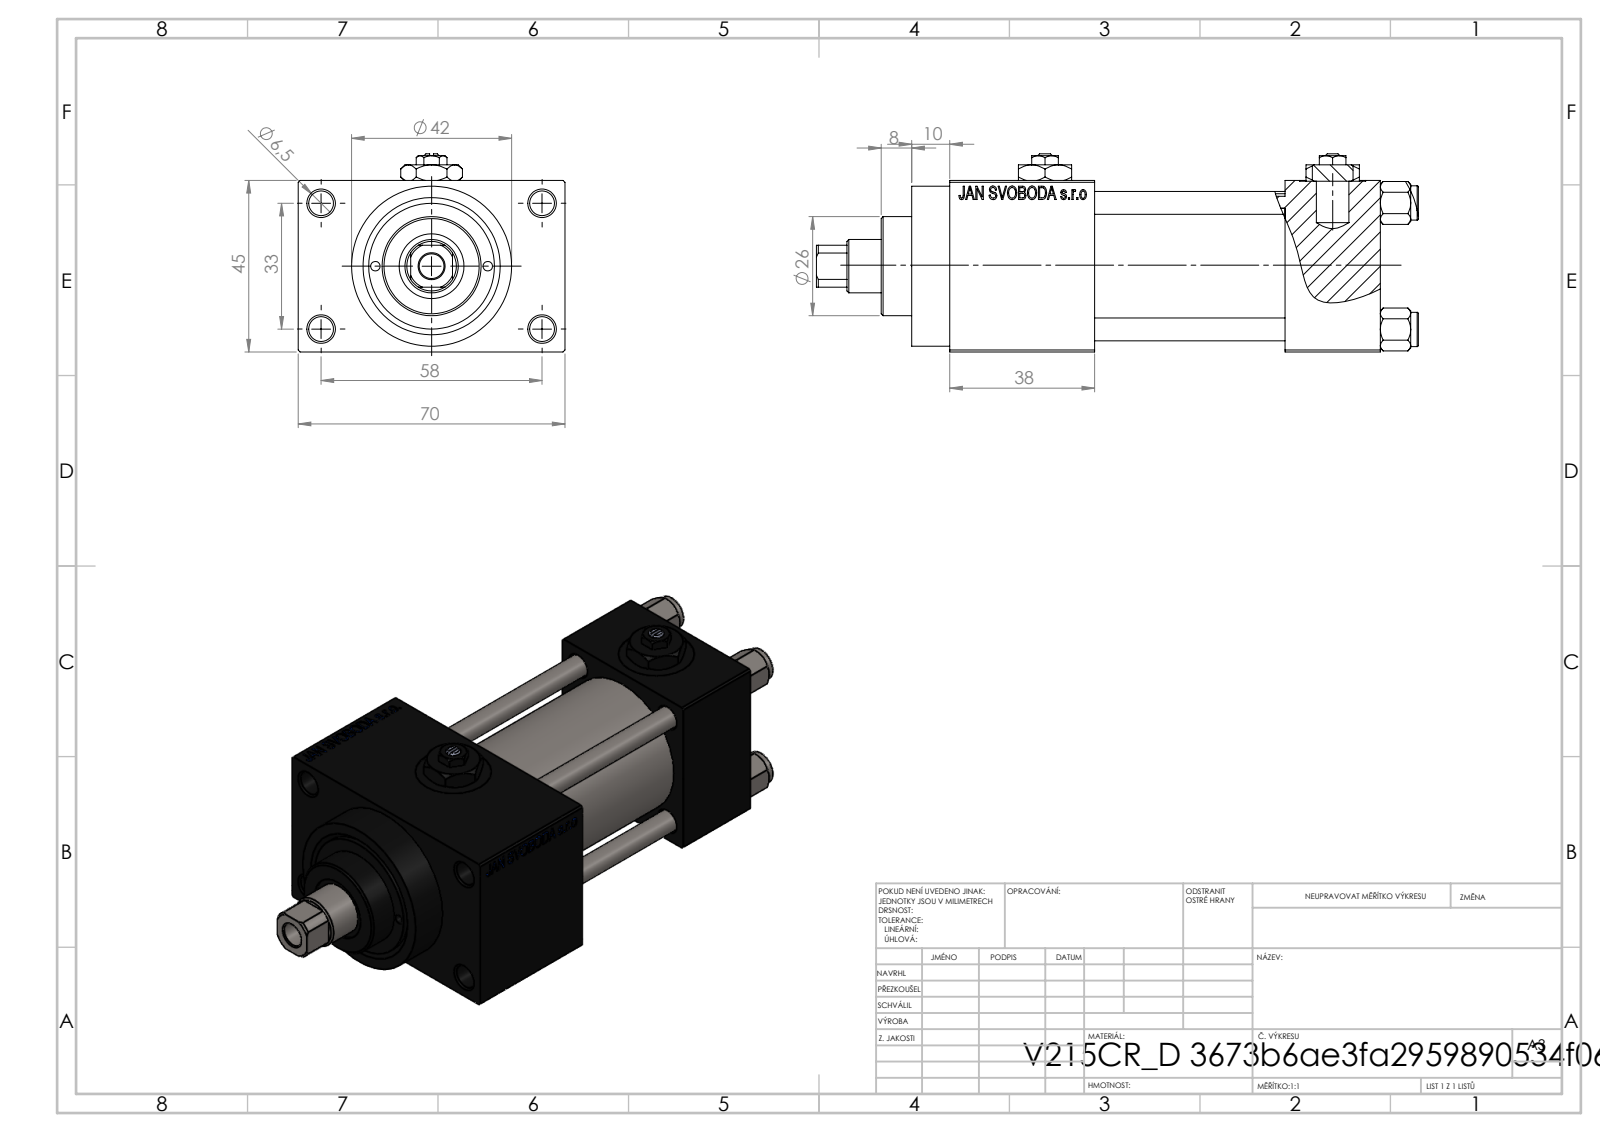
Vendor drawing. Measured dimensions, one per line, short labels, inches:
name: V215CR_D_Body; NUT_M5_D; Zatka_pro_OIL_PORT; V215CR_VCP_D (+2 more)
written by: SolidWorks 2019 (CONFIG_CONTROL_DESIGN)
unit: in
bodies: 13 solids, 1209 faces (544 planar, 103 cylindrical, 562 other)
size: 6.22 × 2.756 × 2.047
volume: 13.97 in³; area: 119.5 in²
holes: 5× ⌀0.256, 4× ⌀0.236, 4× ⌀0.518, 4× ⌀0.787, 3× ⌀0.276, 2× ⌀0.098, 1× ⌀0.551, 1× ⌀0.669, 1× ⌀0.945, 1× ⌀1.26, 1× ⌀1.299
bosses: 4× ⌀0.354, 1× ⌀1.654, 1× ⌀1.496, 1× ⌀1.024
rounds: 1× R0.256
face distances: 1.772, 0.984, 1.969, 0.492, 2.953, 2.264, 3.465, 1.496, 4.449, 2.756
hole spacings: 0.488, 0.657, 0.858, 0.924, 1.307, 1.314, 1.392, 1.396
